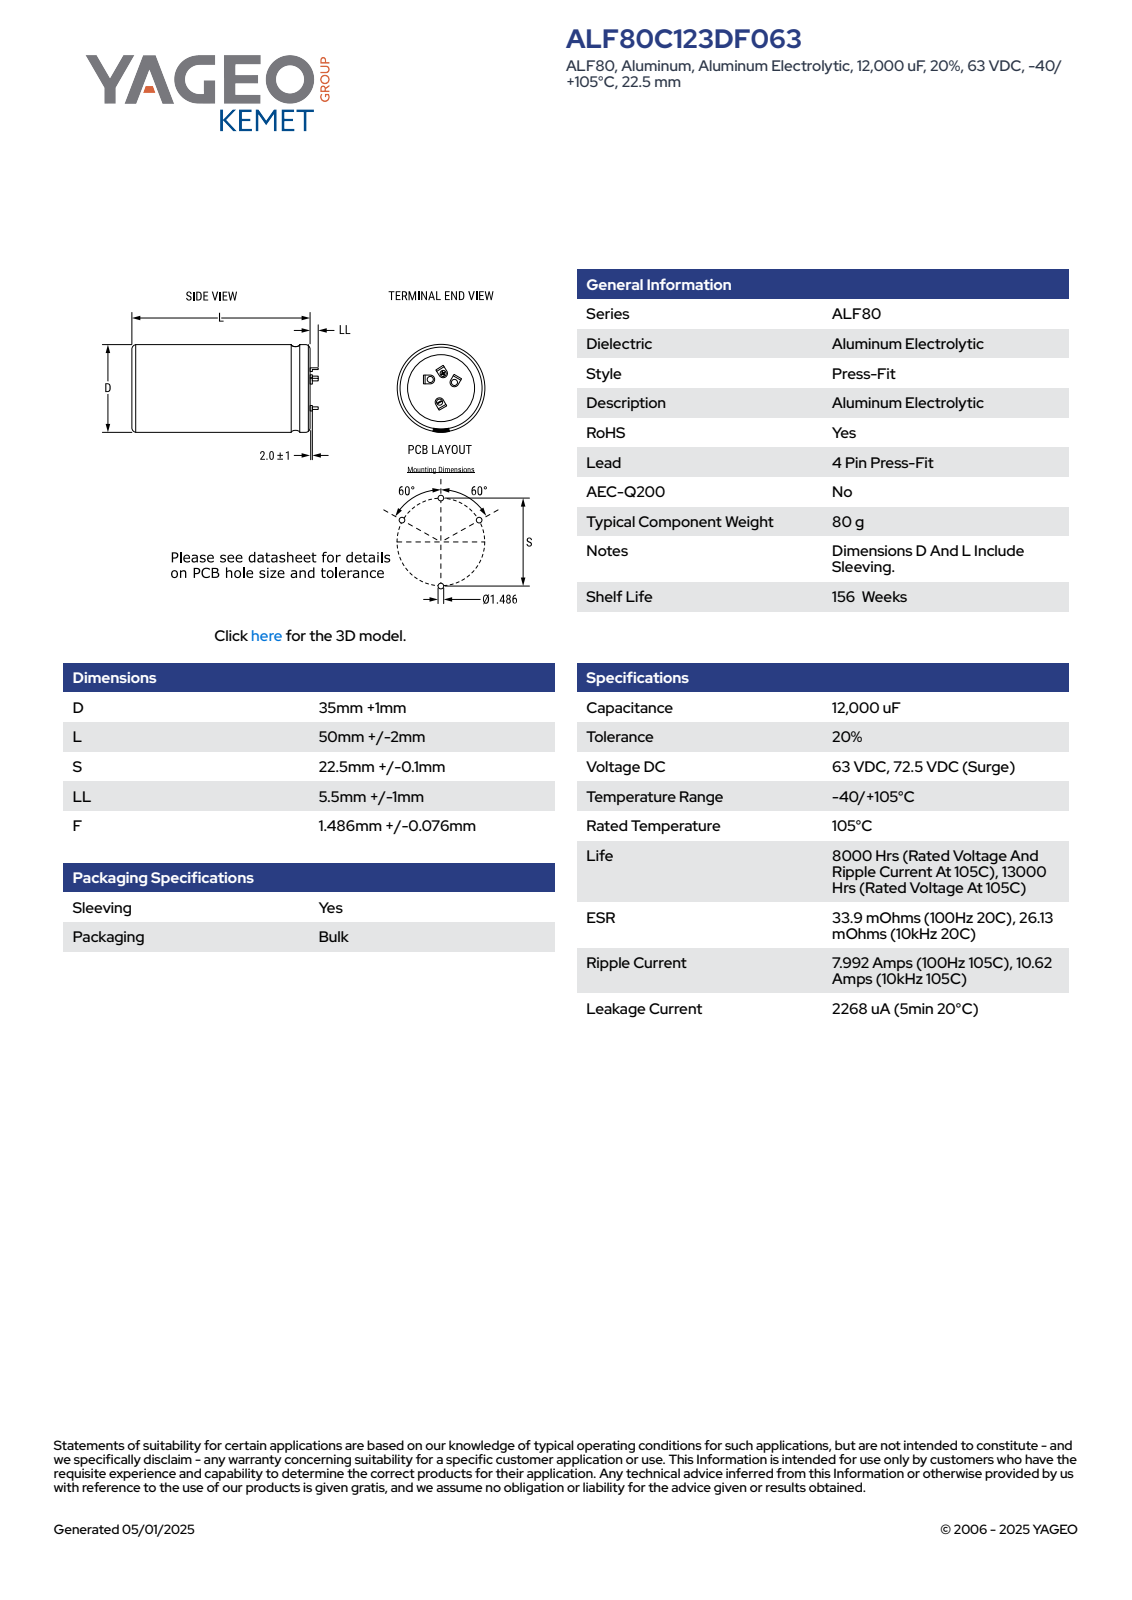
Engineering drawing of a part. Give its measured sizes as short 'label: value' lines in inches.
name: CARS_ALF2040C_35X50_D36L52S22.5LL6.5
written by: SolidWorks 2014 (AUTOMOTIVE_DESIGN)
unit: in
bodies: 6 solids, 333 faces (139 planar, 138 cylindrical, 56 other)
size: 2.308 × 1.417 × 1.417
volume: 3.217 in³; area: 12.7 in²
bosses: 4× ⌀0.138, 1× ⌀1.417
rounds: 50× R0.006, 8× R0.004, 8× R0.017, 3× R0.098, 1× R0.099
face distances: 2.047, 2.048, 0.031, 0.197, 0.118, 0.119, 2.166, 0.197, 0.142, 0.26
